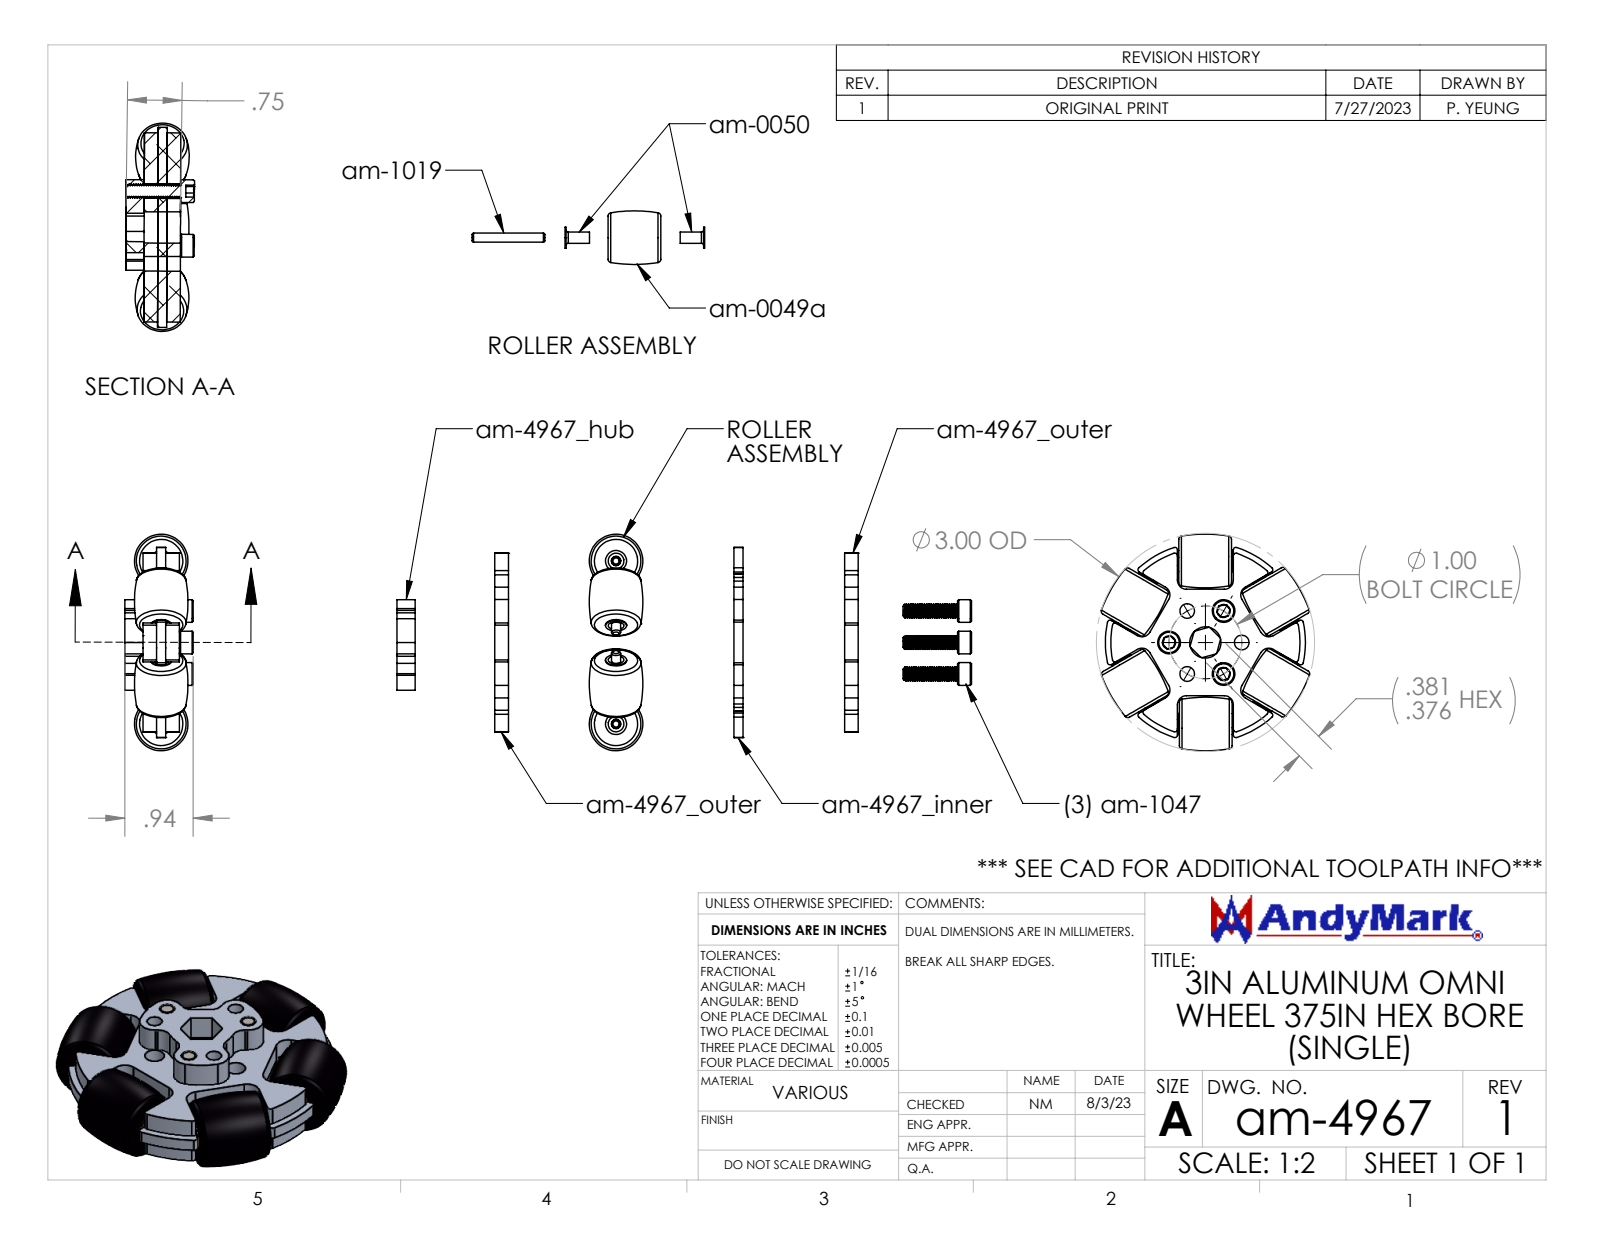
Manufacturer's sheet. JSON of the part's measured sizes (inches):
{"part_name": "am-4967 3IN Aluminum Omni 375IN Hex Bore (Single); 4in Crown Roller Rubber Omni; Bushing Omni; am-4967_hub 3IN Aluminum Omni Wheel 375IN Hex Bore Hub (+5 more)", "step_written_by": "SolidWorks 2022 (AUTOMOTIVE_DESIGN)", "units": "inches", "bodies": {"solids": 31, "faces": 1021, "planar": 212, "cylindrical": 632, "other": 177}, "overall_size": [2.977, 2.867, 0.94], "volume_in3": 3.25, "surface_area_in2": 53.97, "round_holes": [[0.128, 6], [0.153, 6], [0.159, 6], [0.201, 6], [0.43, 1]], "round_bosses_or_shafts": [[0.29, 6], [0.154, 6], [0.125, 6], [0.312, 3], [0.19, 3], [0.149, 3]], "partial_cylinders_radius": [[0.035, 72], [0.125, 18], [0.156, 6], [0.344, 1], [0.656, 1], [1.3, 1], [1.375, 1]], "face_to_face_distances": [0.187, 0.313, 0.125, 0.5, 0.752, 0.018, 0.027, 0.743, 0.725, 0.77], "hole_center_spacings": [0.5, 0.866, 0.707, 0.966, 0.259, 1, 0.259, 2.24]}
